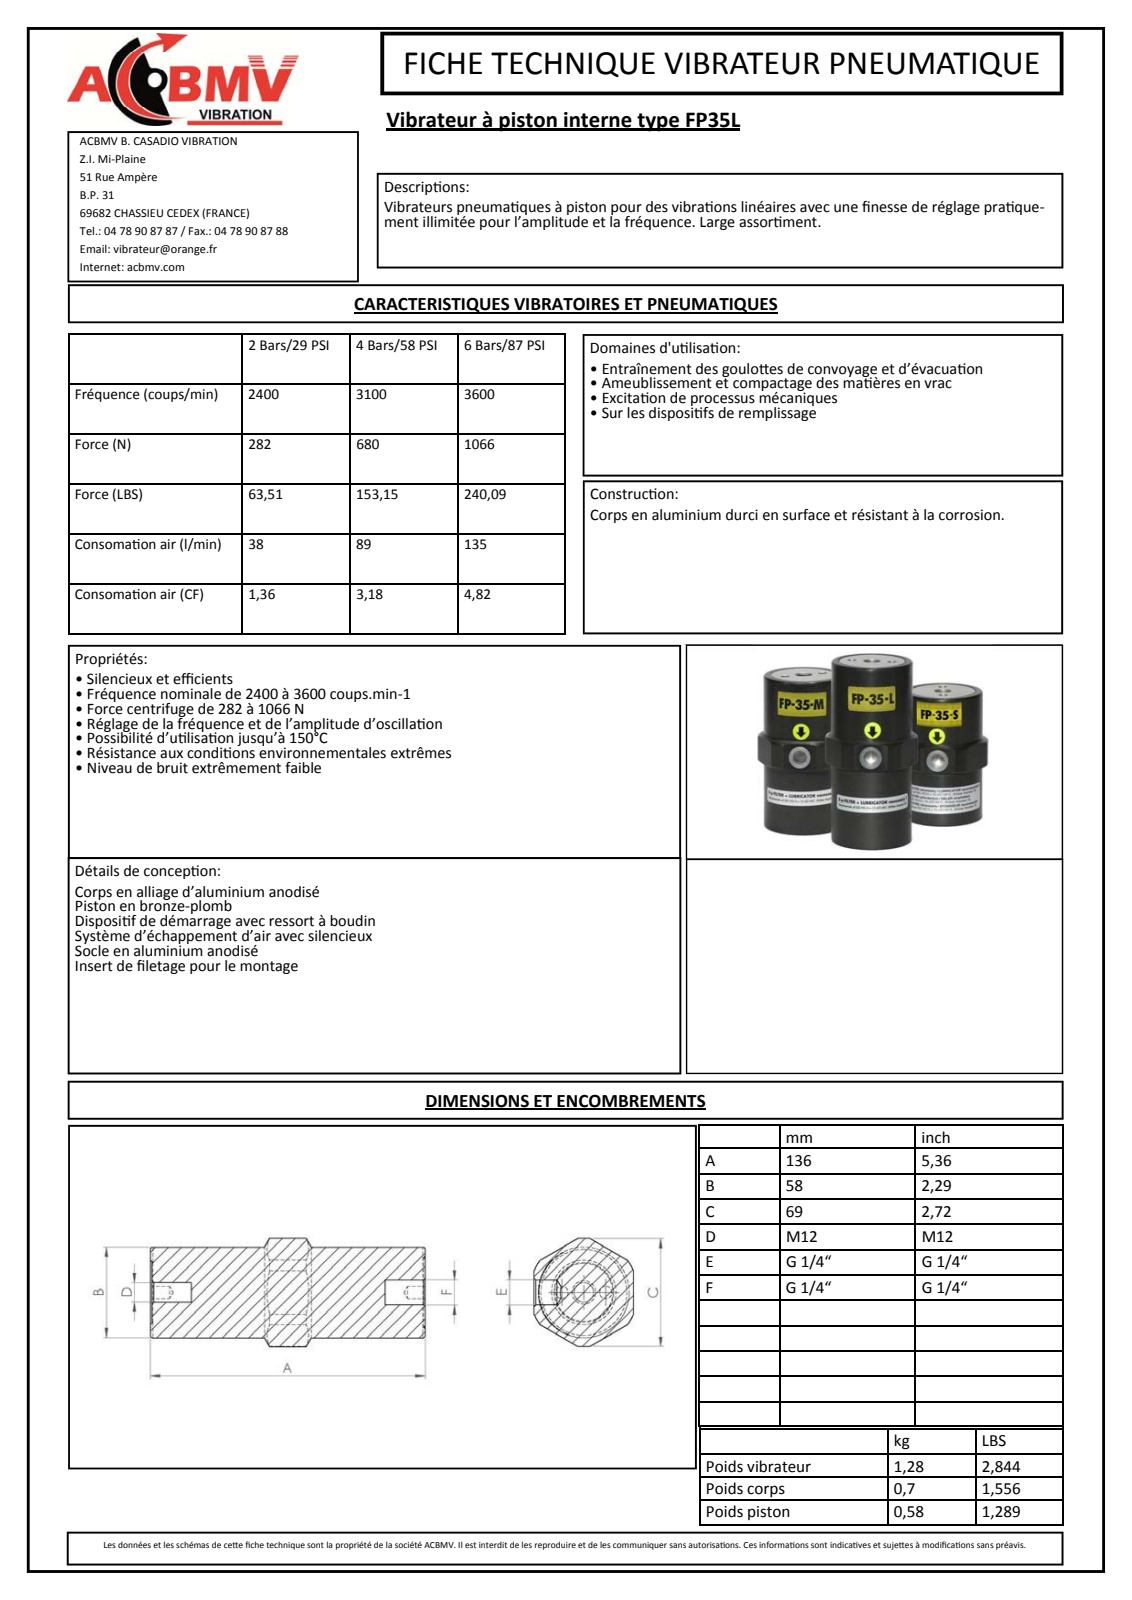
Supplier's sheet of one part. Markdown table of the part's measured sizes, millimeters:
| quantity | value |
| --- | --- |
| part name | 9035-30-M |
| STEP written by | Autodesk Inventor 2011 (CONFIG_CONTROL_DESIGN) |
| units | millimeters |
| bodies | 1 solid, 446 faces (190 planar, 56 cylindrical, 200 other) |
| overall size | 136 × 68.8 × 65 |
| volume | 368 717 mm³ |
| surface area | 33 748 mm² |
| round holes (diameter × count) | 6.2 × 2, 11.45 × 2, 10.11 × 1 |
| round bosses / shafts (diameter × count) | 58 × 1 |
| partial cylindrical surfaces (radius × count) | 19.5 × 1, 28.8 × 1, 29.08 × 1, 29.1 × 1, 34.4 × 1 |
| main face-to-face distances | 135.5, 0.5, 136, 65, 122.3, 121.8, 13.7, 19, 18.5, 103.3 |
| hole center spacings | 15, 30 |
